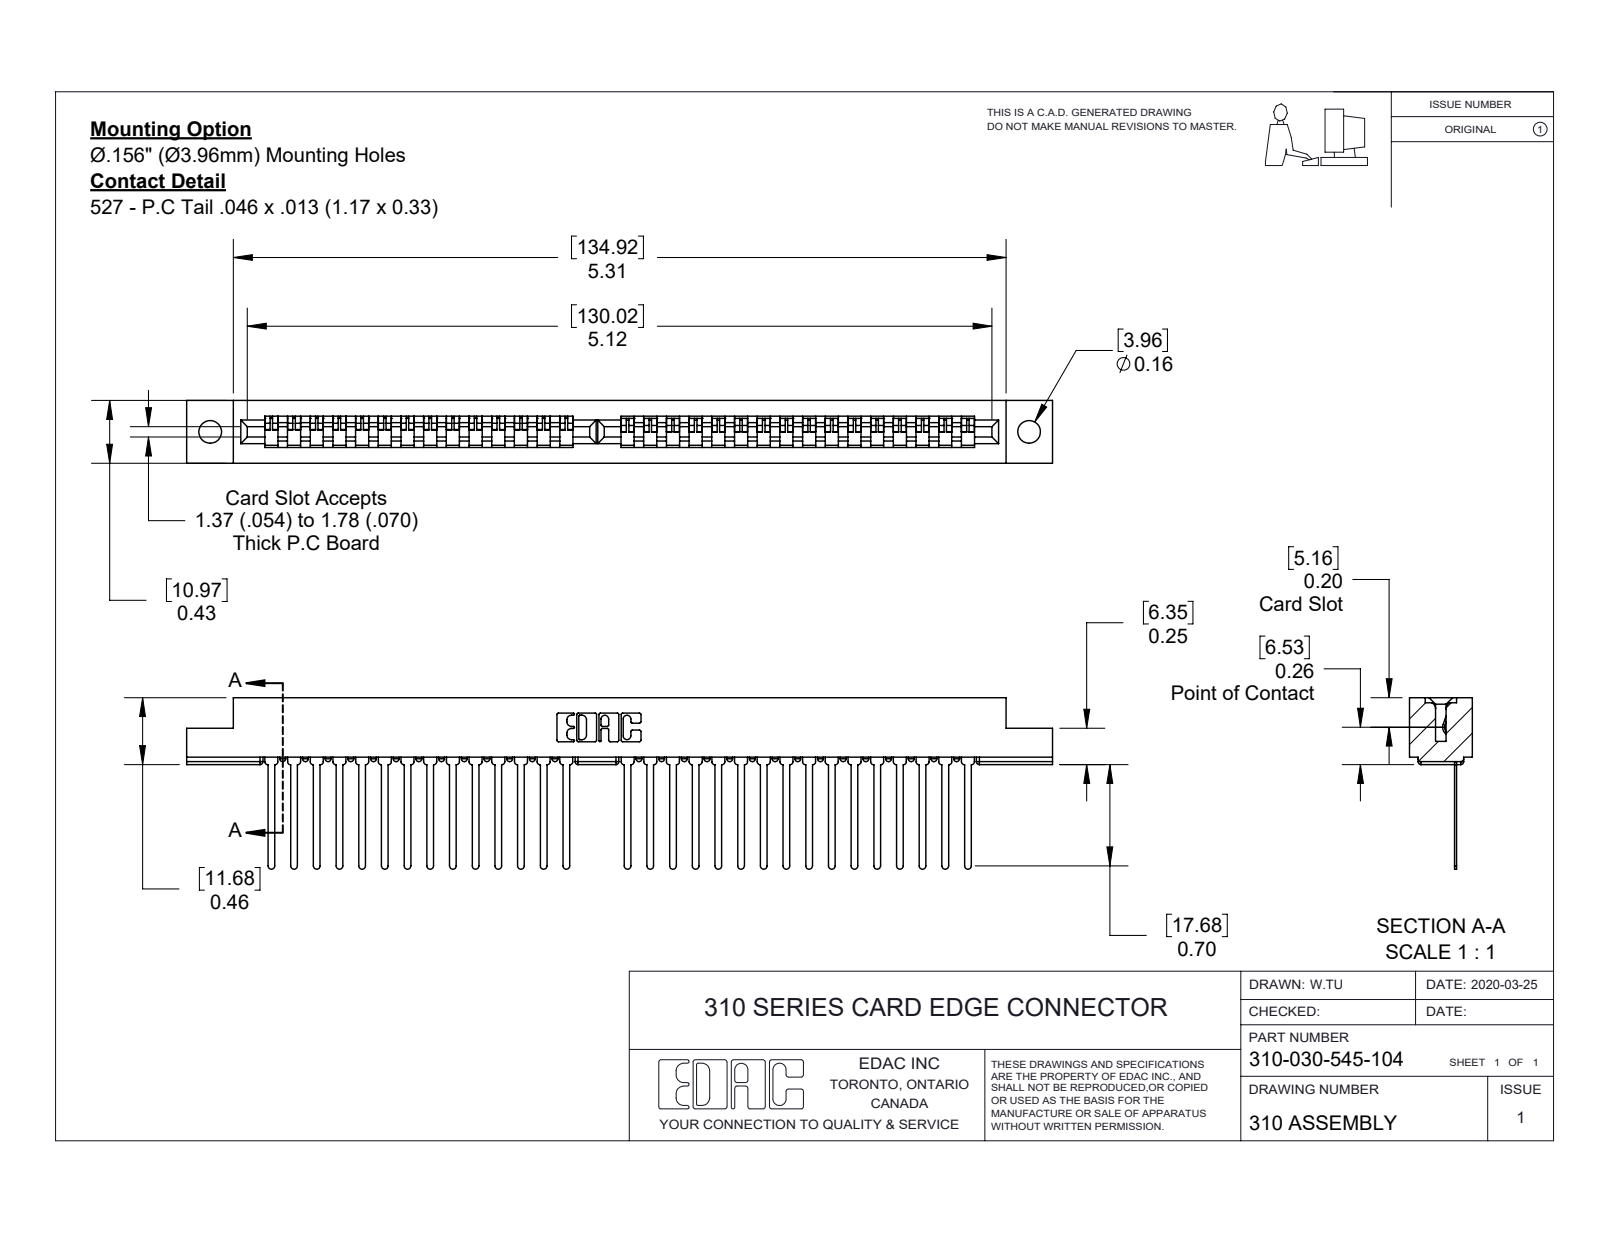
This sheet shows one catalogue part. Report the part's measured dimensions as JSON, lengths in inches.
{"part_name": "310 Part_.156 Dia. Hole; 307-290-001_545; 310-030-545-104", "step_written_by": "SolidWorks 2016 (CONFIG_CONTROL_DESIGN)", "units": "inches", "bodies": {"solids": 31, "faces": 1846, "planar": 1194, "cylindrical": 588, "other": 64}, "overall_size": [5.953, 1.179, 0.432], "volume_in3": 0.775, "surface_area_in2": 24.28, "round_holes": [[0.156, 2]], "partial_cylinders_radius": [[0.02, 158], [0.023, 30], [0.01, 22], [0.007, 6], [0.031, 6], [0.026, 3], [0.012, 2], [0.025, 2]], "face_to_face_distances": [0.109, 0.324, 0.015, 0.013, 0.432, 0.072, 0.124, 0.309, 0.2, 0.409], "hole_center_spacings": [5.63]}
